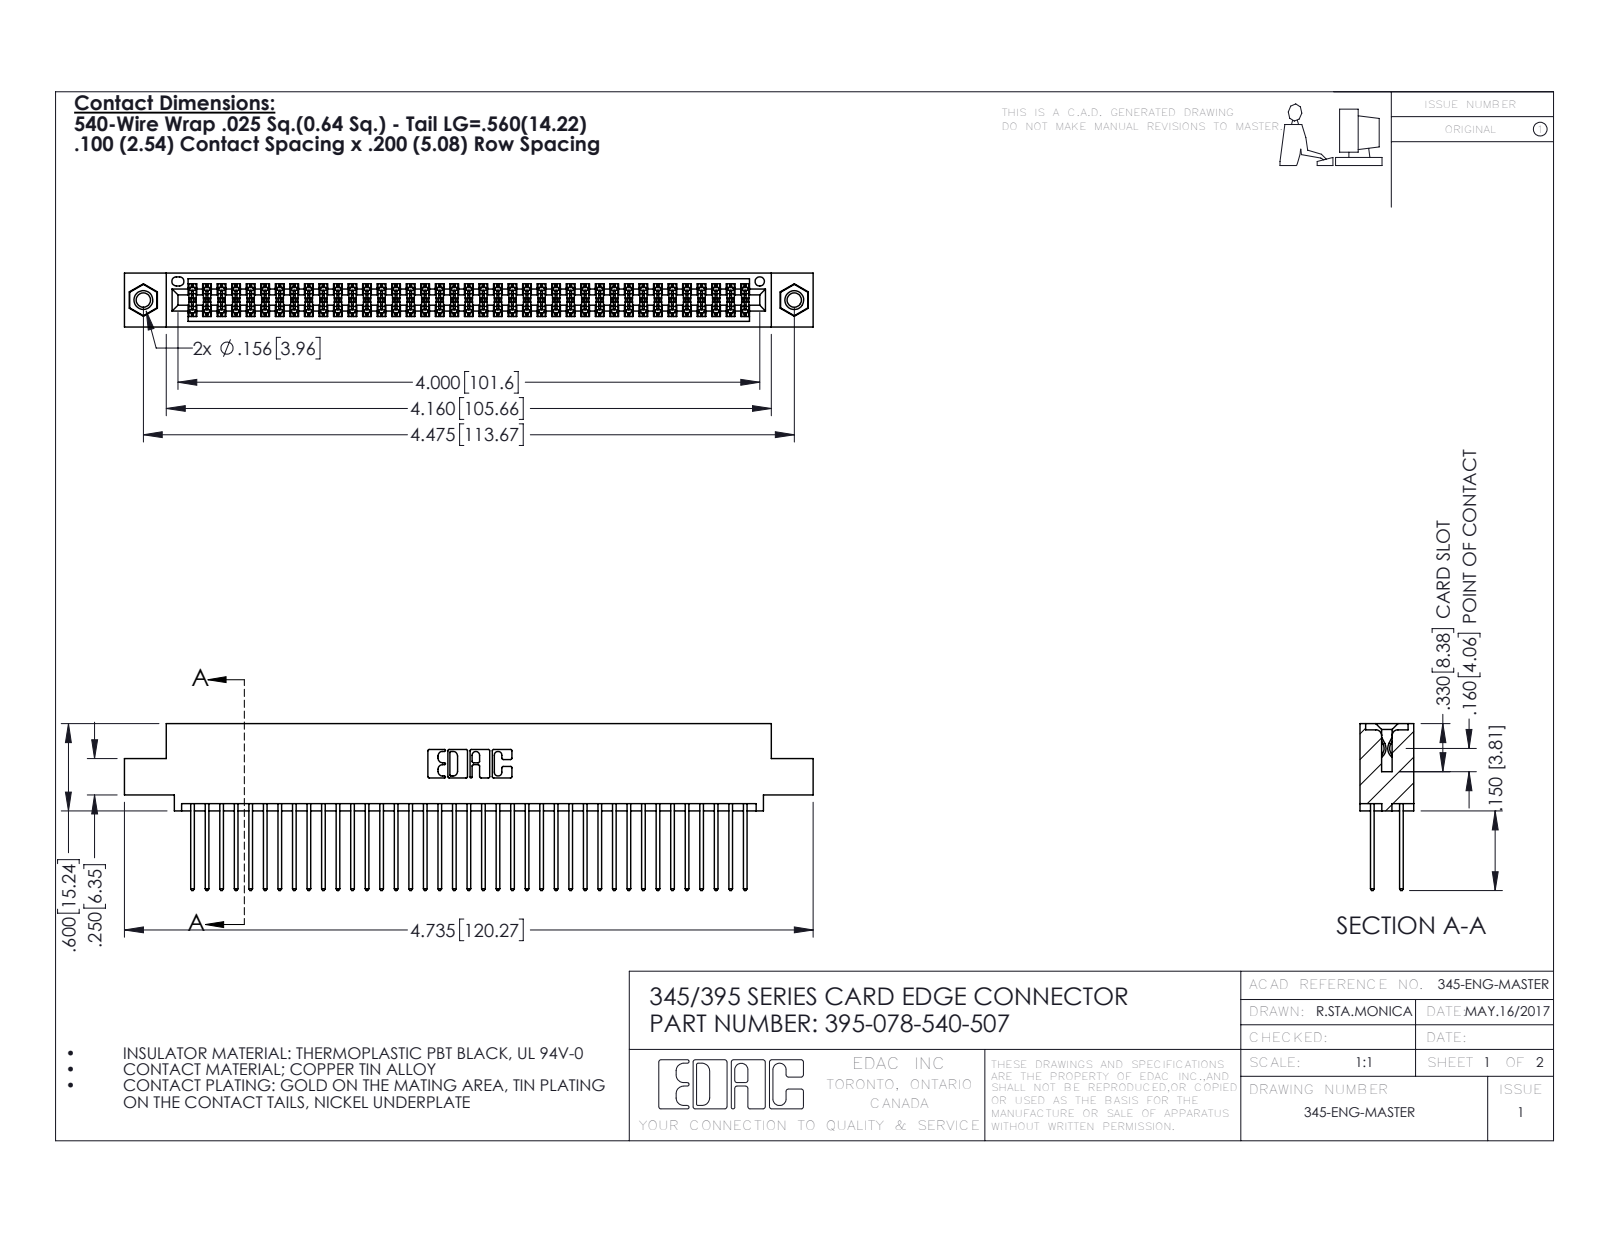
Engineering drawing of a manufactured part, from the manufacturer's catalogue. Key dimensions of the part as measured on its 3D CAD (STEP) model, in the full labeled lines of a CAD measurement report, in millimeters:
Part name (STEP PRODUCT): 345-292-001_345-293-140; 345 Part_0.110 Offset - 0.156 Dia-TI; 345-250-001_345-250-005-103; 395-078-540-507
STEP written by: SolidWorks 2016 (CONFIG_CONTROL_DESIGN)
Units: millimetres
Bodies: 81 solids, 4090 faces (2690 planar, 1384 cylindrical, 16 other)
Overall size (bounding box): 120.3 × 29.1 × 9.4
Volume: 11 900 mm³ · Surface area: 18 970 mm²
Round holes (diameter × count): ⌀2.5 ×2, ⌀3.2 ×2, ⌀4 ×2, ⌀1.6 ×1
Round bosses / shafts (diameter × count): ⌀3.9 ×2
Partial cylindrical surfaces — rounded edges, fillets, slot ends (radius × count): R0.2 ×117, R0.3 ×78, R0.3 ×22, R0.2 ×6, R0.8 ×6, R0.7 ×3, R0.4 ×2, R0.5 ×2
Main face-to-face distances: 1.8, 7.6, 5.1, 2.5, 6.9, 0.6, 9.4, 5.7, 4.4, 3.8
Hole centre spacings: 6.9, 107.7, 113.7
